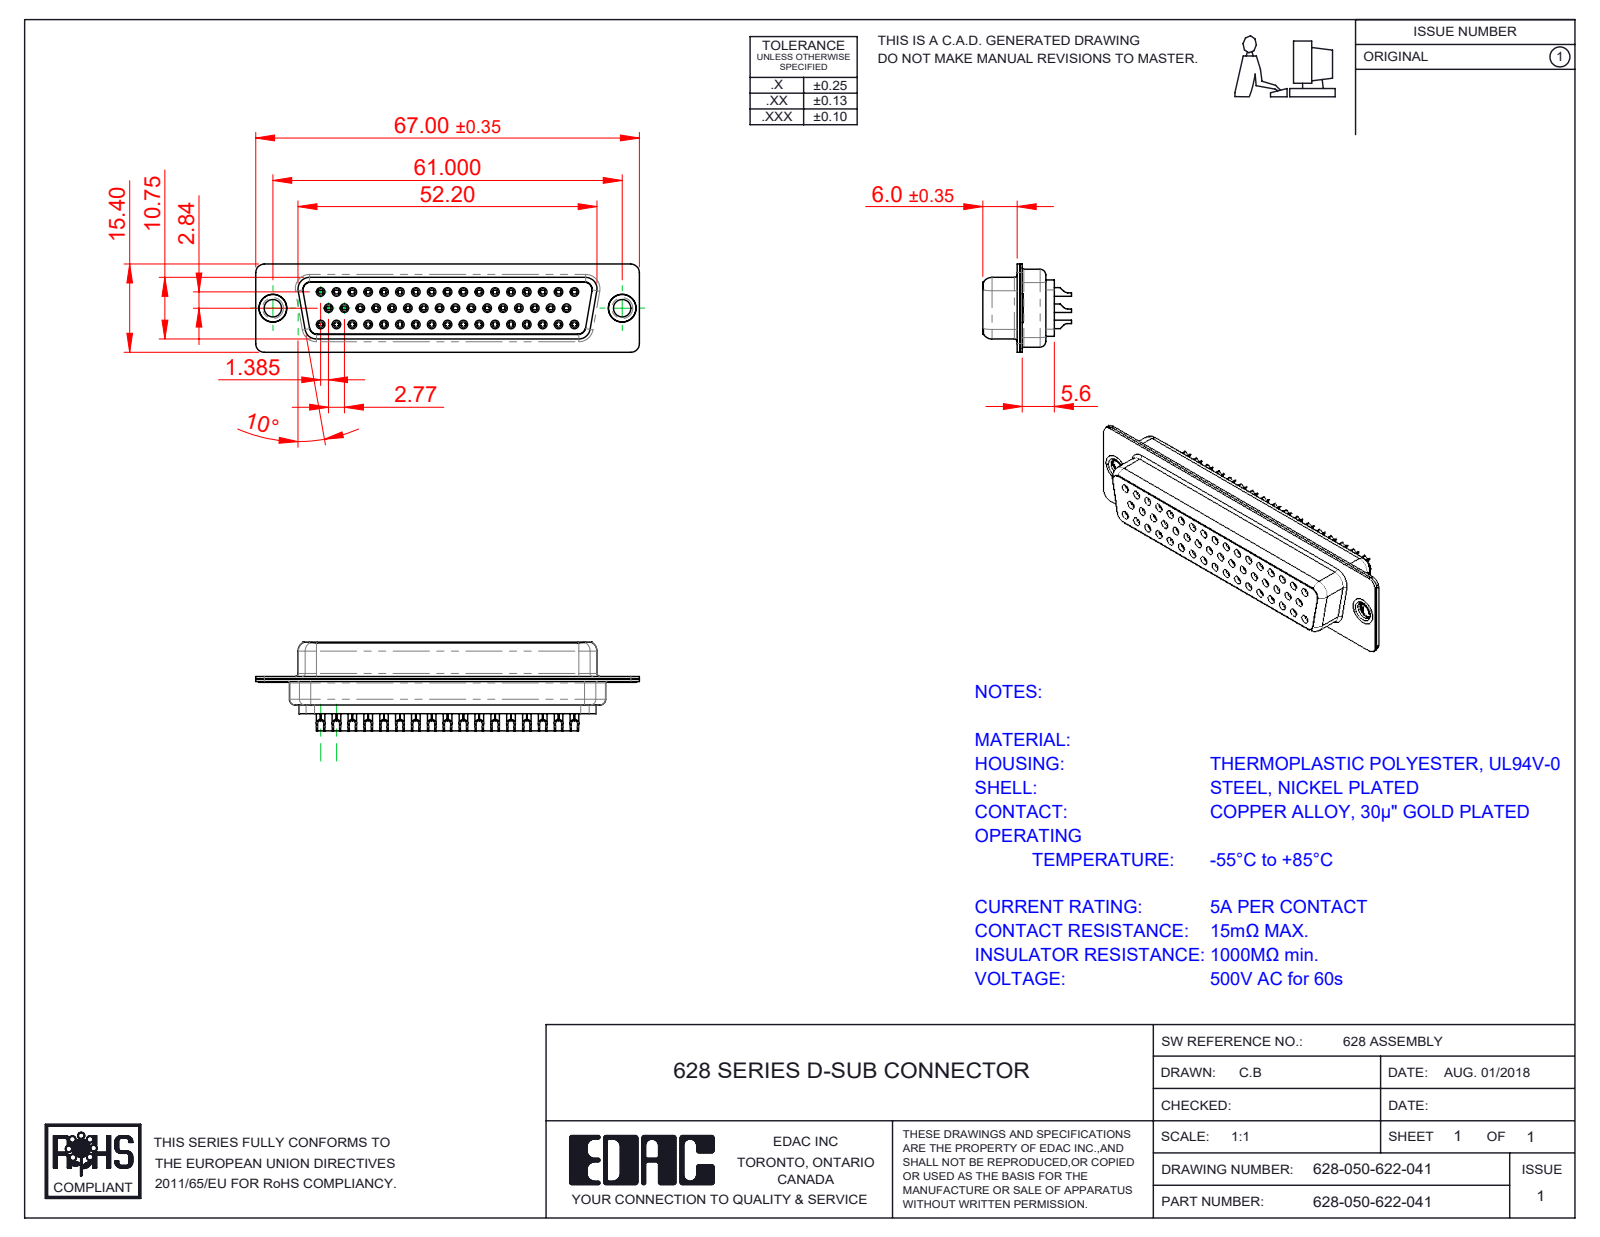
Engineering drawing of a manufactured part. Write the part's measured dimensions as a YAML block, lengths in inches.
part_name: "628-050-622-041; 628 Contact Row 2_22M; 628 Contact Row 1_22L; 628 Shell Front_50 Contacts (+4 more)"
step_written_by: "SolidWorks 2020 (CONFIG_CONTROL_DESIGN)"
units: inches
bodies: {solids: 55, faces: 4703, planar: 1117, cylindrical: 1371, other: 2215}
overall_size: [2.638, 0.61, 0.606]
volume: 0.408
surface_area: 23.98
round_holes:
  - {diameter: 0.031, count: 50}
  - {diameter: 0.035, count: 50}
  - {diameter: 0.043, count: 50}
  - {diameter: 0.063, count: 50}
  - {diameter: 0.067, count: 17}
  - {diameter: 0.12, count: 2}
  - {diameter: 0.157, count: 2}
  - {diameter: 0.159, count: 2}
  - {diameter: 0.191, count: 2}
round_bosses_or_shafts:
  - {diameter: 0.079, count: 50}
  - {diameter: 0.059, count: 50}
  - {diameter: 0.047, count: 50}
  - {diameter: 0.197, count: 2}
  - {diameter: 0.195, count: 2}
  - {diameter: 0.189, count: 2}
  - {diameter: 0.14, count: 2}
partial_cylinders:
  - {radius: 0.011, count: 33}
  - {radius: 0.059, count: 16}
  - {radius: 0.079, count: 12}
  - {radius: 0.053, count: 8}
  - {radius: 0.039, count: 7}
  - {radius: 0.01, count: 4}
  - {radius: 0.02, count: 4}
  - {radius: 0.024, count: 4}
face_to_face_distances: [0.018, 0.016, 0.446, 0.074, 0.035, 0.238, 0.256, 0.406, 0.492, 0.254]
hole_center_spacings: [0.124, 0.109, 0.218, 0.327, 0.436, 0.545, 0.654, 0.763]
